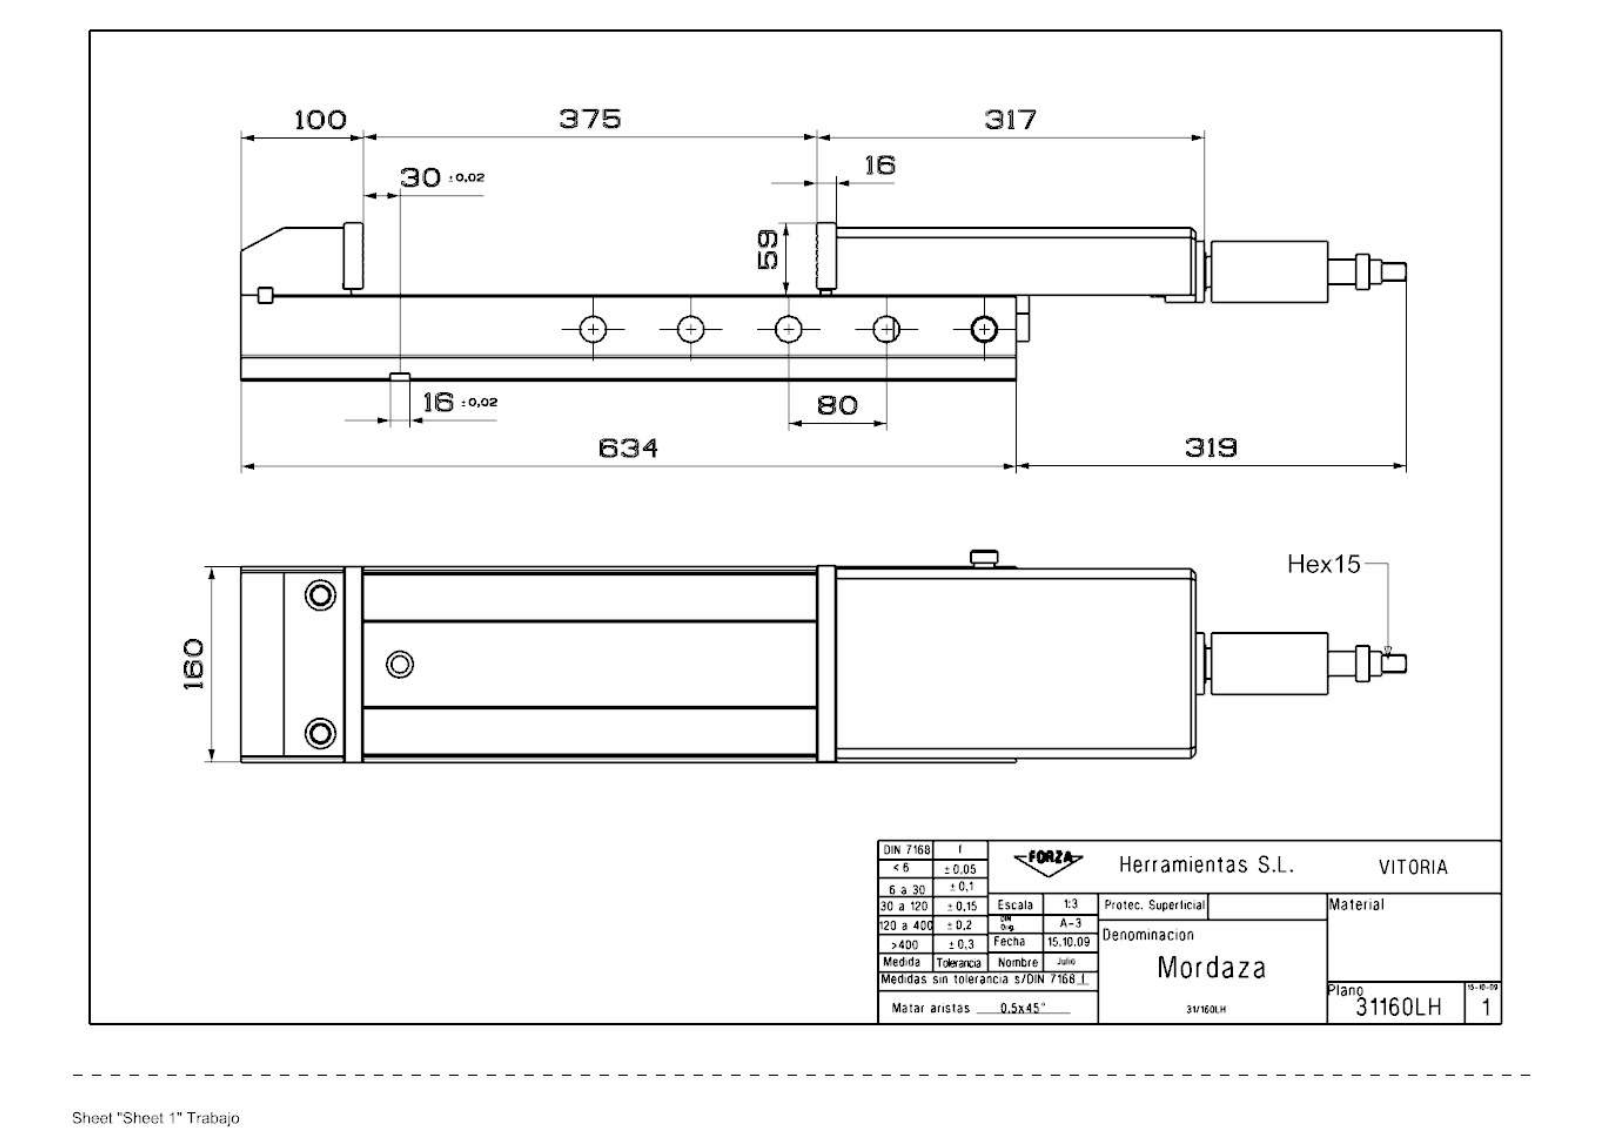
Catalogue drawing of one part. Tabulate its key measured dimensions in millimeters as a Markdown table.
| quantity | value |
| --- | --- |
| part name | 31_160HL_Mordaza |
| STEP written by | SIEMENS PLM Software NX 9.0 (CONFIG_CONTROL_DESIGN) |
| units | millimeters |
| bodies | 14 solids, 466 faces (311 planar, 96 cylindrical, 59 other) |
| overall size | 953 × 173 × 129 |
| volume | 7 869 000 mm³ |
| surface area | 863 936 mm² |
| round holes (diameter × count) | 22 × 9, 5.19 × 6, 6.99 × 4, 9 × 4, 14 × 4, 14.38 × 4, 17 × 4, 8.78 × 2, 11 × 2, 12.38 × 2, 15 × 2, 25 × 2 |
| round bosses / shafts (diameter × count) | 50 × 1, 46 × 1, 41 × 1, 38 × 1, 37 × 1, 32 × 1, 29.5 × 1, 29 × 1 |
| partial cylindrical surfaces (radius × count) | 10 × 4, 2 × 2, 6.5 × 2, 8 × 2, 25 × 1, 32 × 1 |
| main face-to-face distances | 70, 125, 41, 29, 55, 96, 155, 5, 150, 30 |
| hole center spacings | 80, 41.48, 0.66, 160, 4, 4.05, 17.03, 19.85 |
